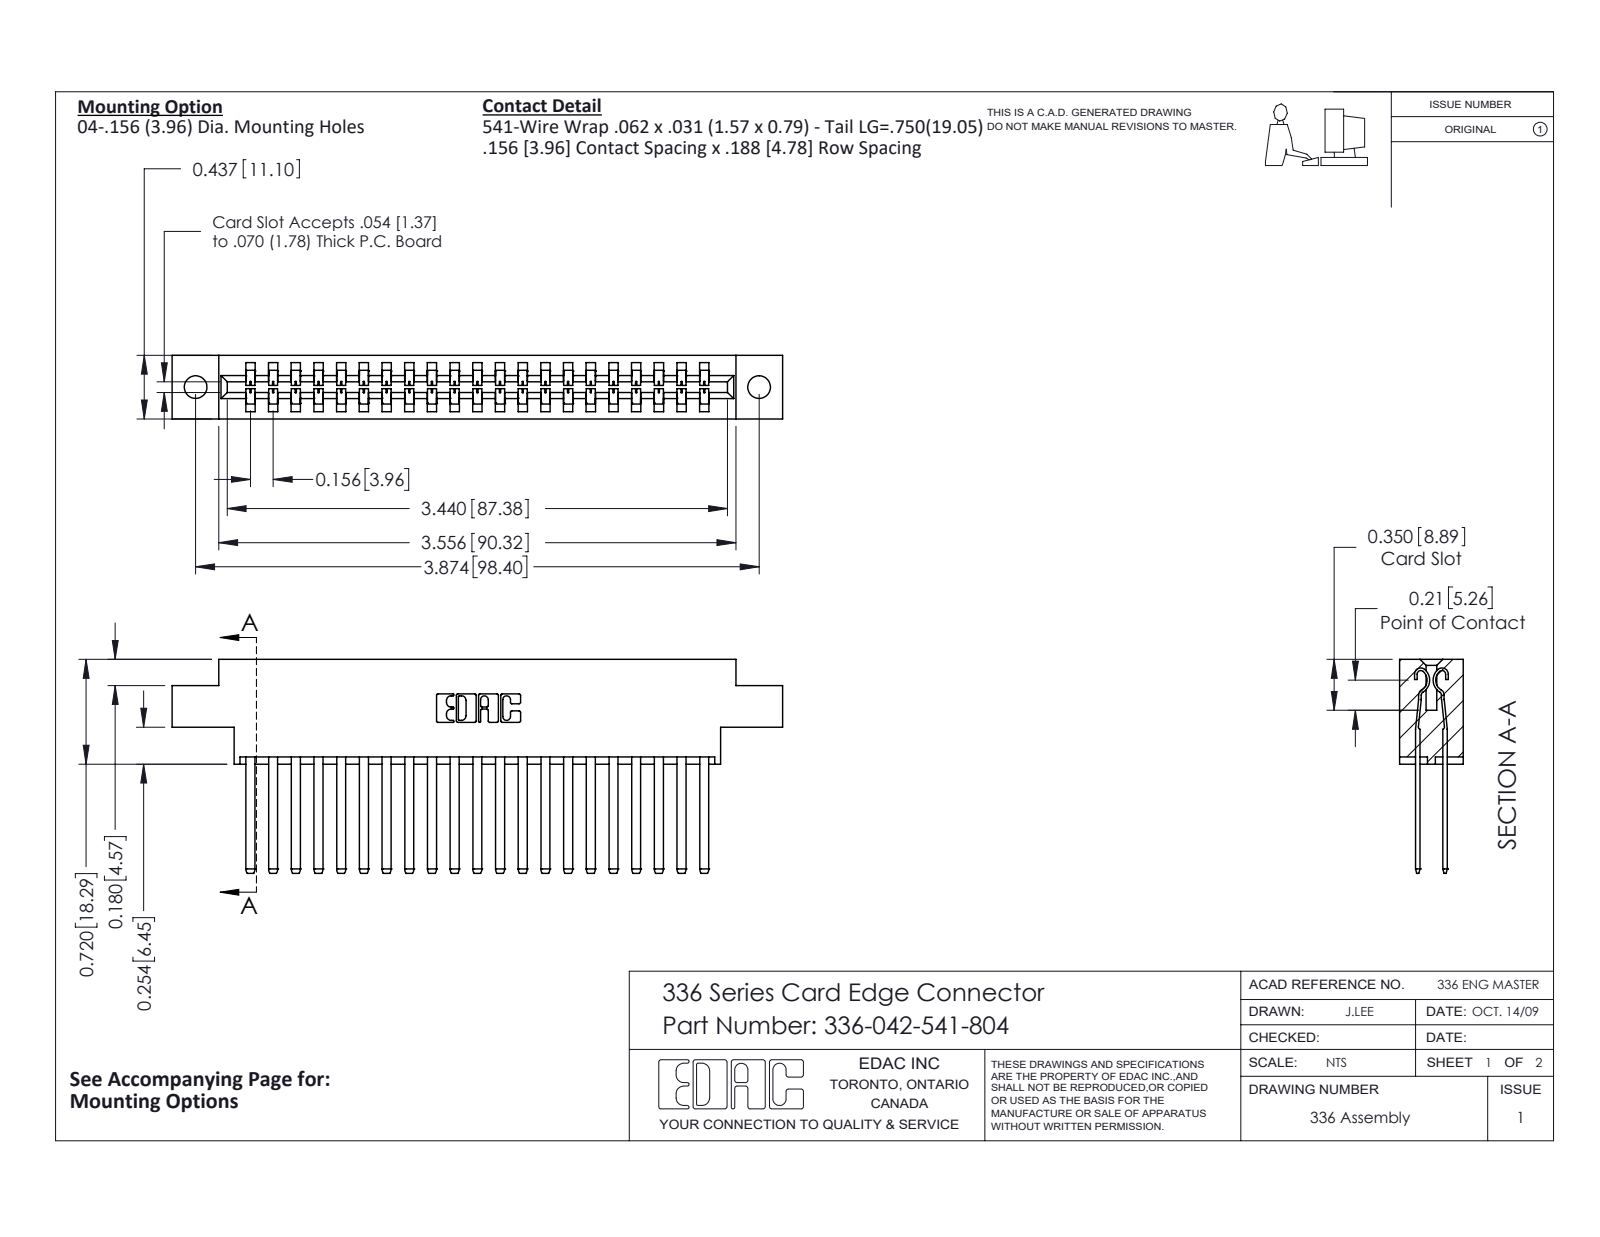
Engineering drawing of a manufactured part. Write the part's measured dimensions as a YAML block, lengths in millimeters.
part_name: "336-042-541-804; 336-290-001_336-290-541; 336 Part_Offset - .156 Dia - TH"
step_written_by: "SolidWorks 2020 (CONFIG_CONTROL_DESIGN)"
units: millimeters
bodies: {solids: 43, faces: 1882, planar: 1166, cylindrical: 716, other: 0}
overall_size: [106.6, 37.3, 11.1]
volume: 15700
surface_area: 19520
round_holes:
  - {diameter: 4, count: 2}
partial_cylinders:
  - {radius: 0.1, count: 84}
  - {radius: 1.4, count: 42}
  - {radius: 0.3, count: 22}
  - {radius: 0.2, count: 6}
  - {radius: 0.8, count: 6}
  - {radius: 0.6, count: 4}
  - {radius: 1, count: 4}
  - {radius: 0.7, count: 3}
face_to_face_distances: [4.8, 8.3, 3.6, 7.5, 2.8, 0.8, 11.1, 0.8, 4.6, 6.5]
hole_center_spacings: [98.4]
